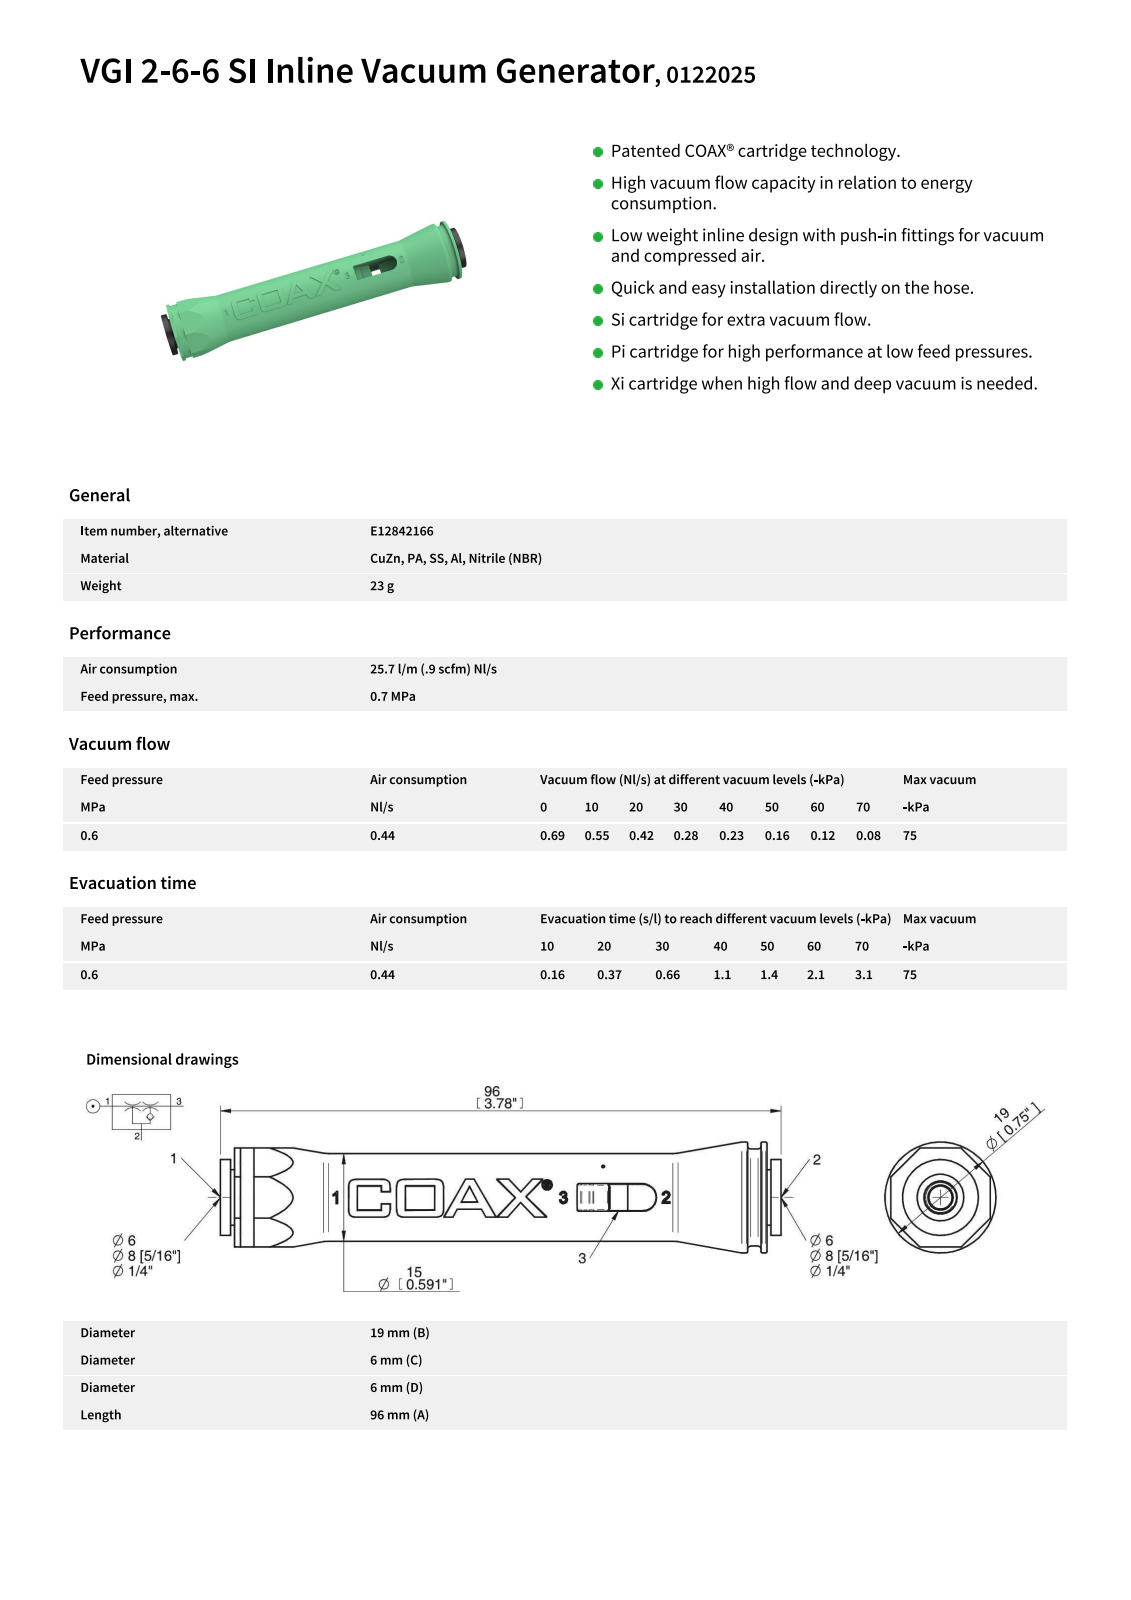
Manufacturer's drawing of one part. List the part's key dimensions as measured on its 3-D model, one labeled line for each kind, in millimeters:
Part name (STEP PRODUCT): 0122198
STEP written by: Unknown (automotive_design)
Units: millimetres
Bodies: 1 solid, 184 faces (101 planar, 34 cylindrical, 49 other)
Overall size (bounding box): 106 × 19 × 19
Volume: 18 370 mm³ · Surface area: 6 382 mm²
Round holes (diameter × count): ⌀6 ×1
Round bosses / shafts (diameter × count): ⌀19 ×1, ⌀17 ×1, ⌀16.75 ×1, ⌀15 ×1, ⌀13 ×1, ⌀10.58 ×1, ⌀7.5 ×1
Partial cylindrical surfaces — rounded edges, fillets, slot ends (radius × count): R0.2 ×4, R7.75 ×1
Main face-to-face distances: 3.3, 17, 92.7, 5, 1, 6, 87.7, 96, 7.5, 98.5
